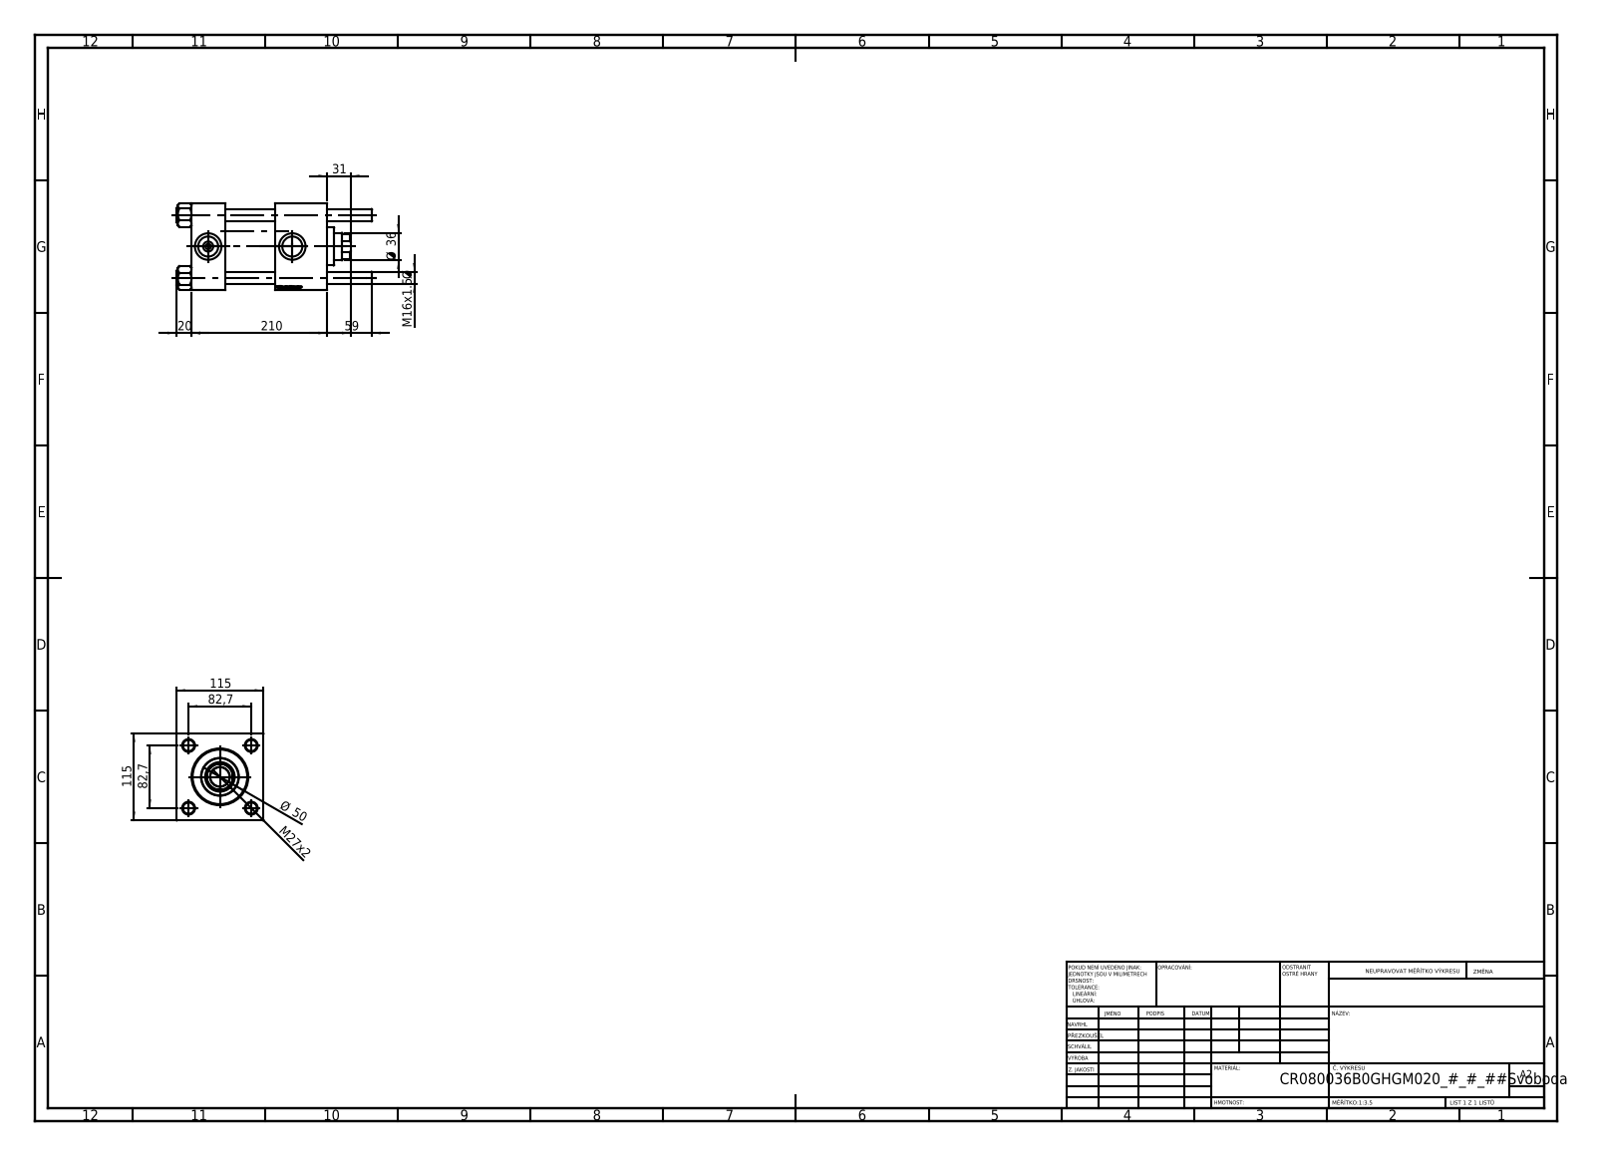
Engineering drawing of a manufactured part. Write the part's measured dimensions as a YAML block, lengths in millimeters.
part_name: "NUT_M5_B; V215CR_VCP_B; V215CR_B_TYCINKA; V215CR_B-1 (+1 more)"
step_written_by: "SolidWorks 2019 (CONFIG_CONTROL_DESIGN)"
units: millimeters
bodies: {solids: 11, faces: 1206, planar: 480, cylindrical: 78, other: 648}
overall_size: [258, 115, 115]
volume: 1866000
surface_area: 294342
round_holes:
  - {diameter: 16, count: 4}
  - {diameter: 7, count: 2}
  - {diameter: 26.44, count: 2}
  - {diameter: 35, count: 2}
  - {diameter: 25.5, count: 1}
  - {diameter: 36, count: 1}
  - {diameter: 39, count: 1}
  - {diameter: 61, count: 1}
  - {diameter: 72, count: 1}
  - {diameter: 80, count: 1}
round_bosses_or_shafts:
  - {diameter: 19, count: 4}
  - {diameter: 86, count: 1}
  - {diameter: 50, count: 1}
partial_cylinders:
  - {radius: 17.5, count: 1}
face_to_face_distances: [115, 44, 110, 179, 135, 69, 66, 20, 150.3, 106.3]
hole_center_spacings: [58.48, 82.7, 116.96, 111]
